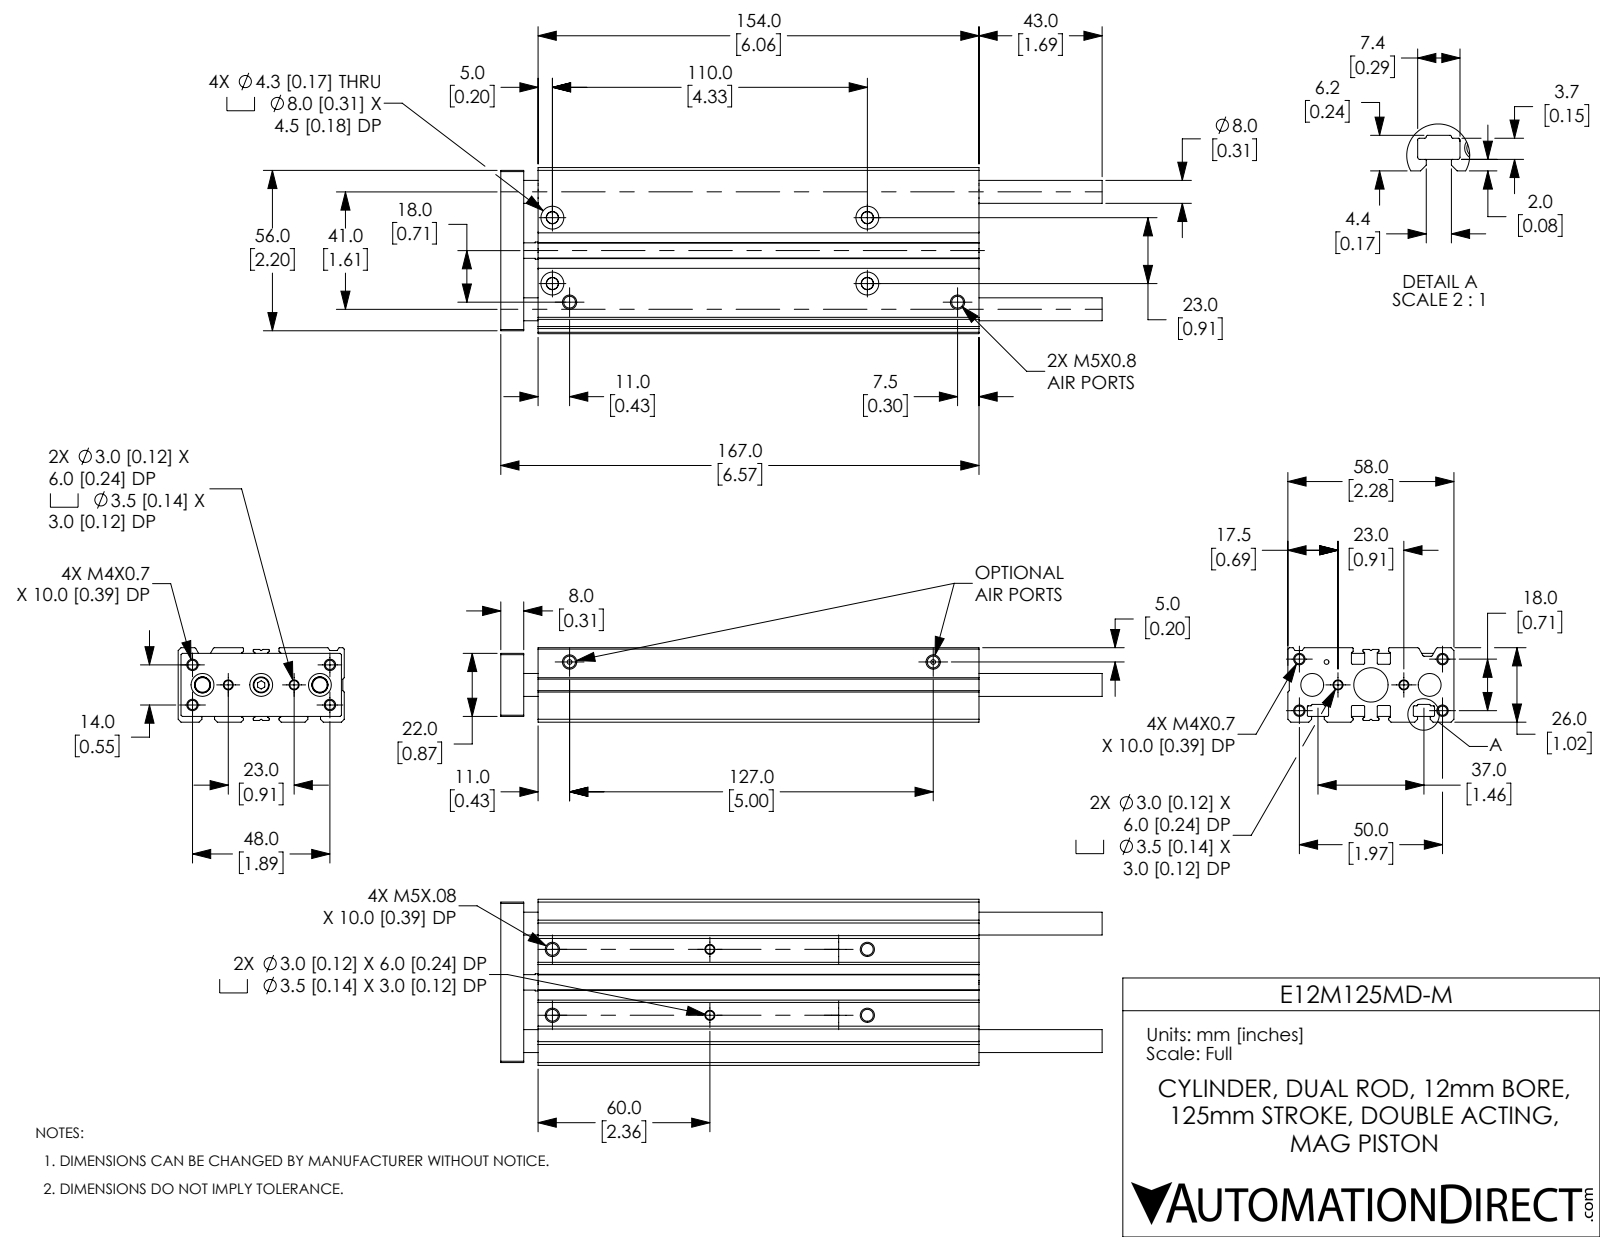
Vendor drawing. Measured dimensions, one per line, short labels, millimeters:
name: E12M125MD-M_ENDPLATE; E12M125MD-D_BODY; E12M125MD-M
written by: SolidWorks 2019 (CONFIG_CONTROL_DESIGN)
unit: mm
bodies: 5 solids, 413 faces (137 planar, 188 cylindrical, 88 other)
size: 210 × 58 × 26
volume: 200 580 mm³; area: 76 076 mm²
holes: 8× ⌀3.24, 8× ⌀4.13, 7× ⌀8, 4× ⌀3, 4× ⌀3.5, 4× ⌀4.3, 3× ⌀1.67, 3× ⌀4, 2× ⌀5.59, 1× ⌀8, 1× ⌀12, 1× ⌀12
bosses: 1× ⌀6, 1× ⌀5.59
rounds: 20× R0.4, 18× R0.2, 8× R0.25, 6× R0.3, 4× R0.5
face distances: 26, 58, 5.8, 9, 20.2, 26.8, 31.2, 22.2, 35.8, 4.6
hole spacings: 2.24, 7.83, 10.06, 14.33, 16.03, 16.22, 23, 25
